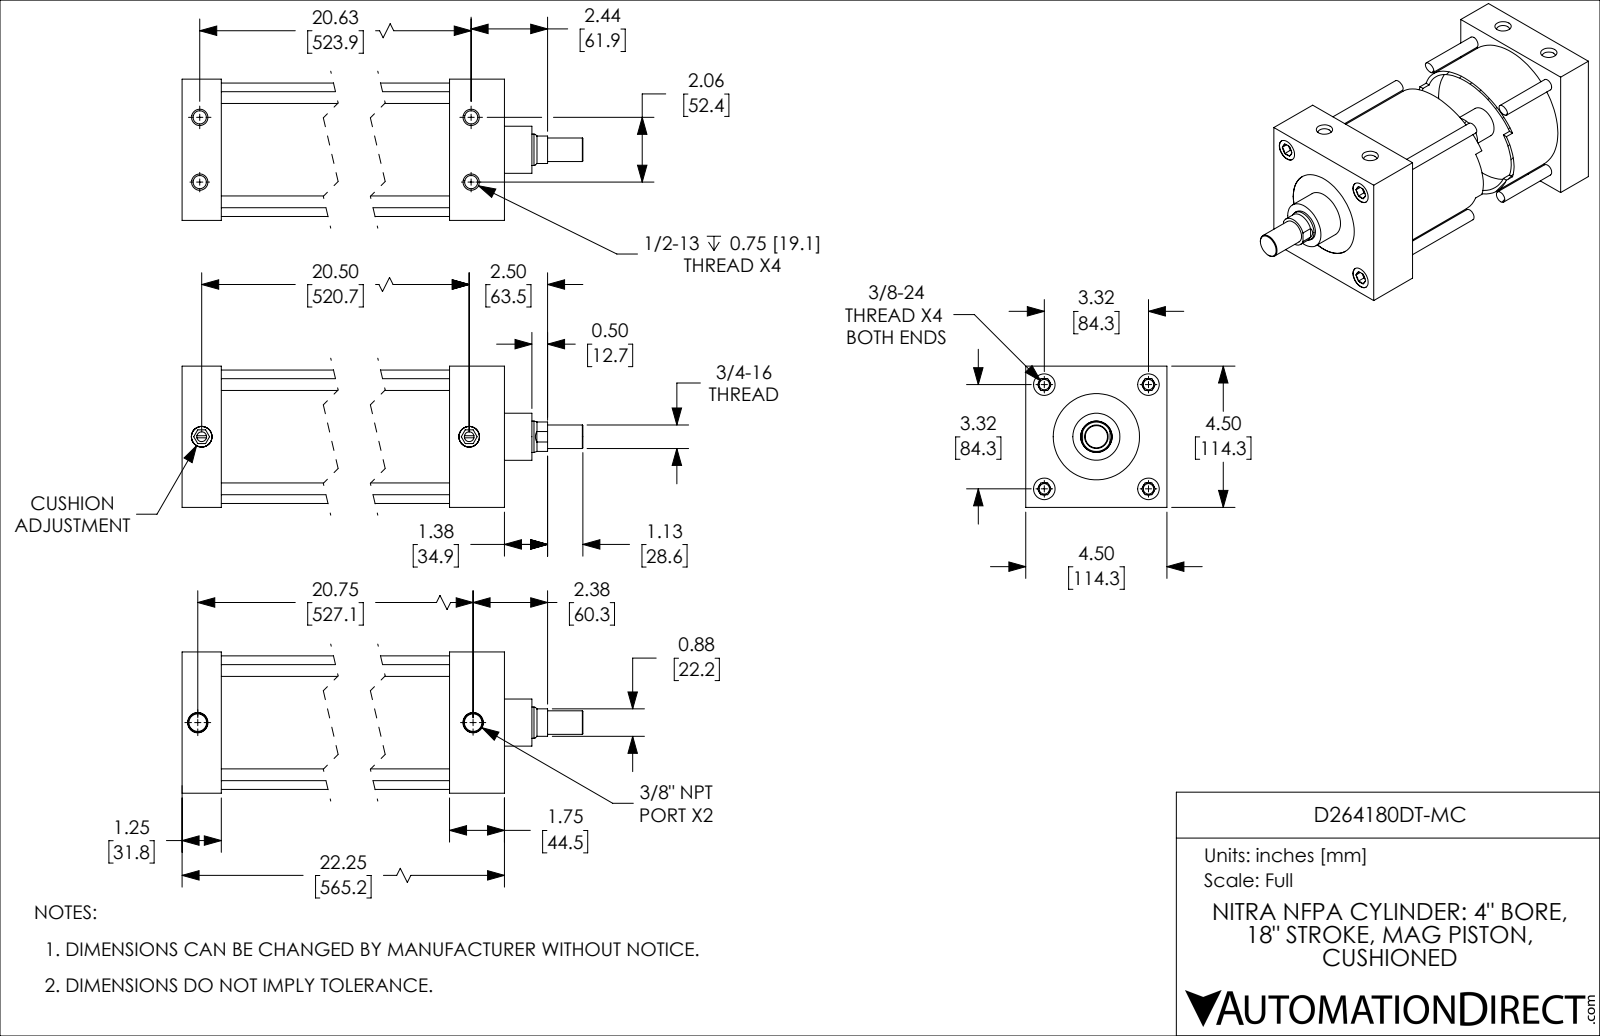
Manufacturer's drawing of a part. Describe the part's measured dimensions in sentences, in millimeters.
The part is named "D264180DT-MC_PISTON_KK1; D264180DT-MC; D264180DT-MC_BODY; D264180DT-MC_CUSHION". Its 3-D file was written by "SolidWorks 2019 (CONFIG_CONTROL_DESIGN)". It is 4 solids with 246 faces: 90 planar, 78 cylindrical and 78 other. Overall it measures 628.7 by 114.3 by 114.3 millimeters. Its volume is 2 134 000 cubic millimeters and its surface area 557 900 square millimeters. Round holes: 4 of diameter 8.4, 4 of diameter 10.7, 4 of diameter 17.4, 2 of diameter 7.9, 2 of diameter 14.3, 2 of diameter 16.7, 1 of diameter 25.4, 1 of diameter 69.9, 1 of diameter 101.6. Round bosses or shafts: 4 of diameter 9.5, 2 of diameter 16.7, 1 of diameter 108, 1 of diameter 101.6, 1 of diameter 38.1, 1 of diameter 25.4, 1 of diameter 19.1. Partial cylindrical surfaces (rounded edges, fillets, slot ends): 1 of radius 11.9. The main face-to-face distances are 31.8, 114.3, 520.7, 489, 565.2, 533.4, 44.5, 63.5, 457.2, 501.7. The hole center spacings are 26.2, 59.6, 84.3, 526.1, 52.4, 119.3, 523.9, 526.5.
